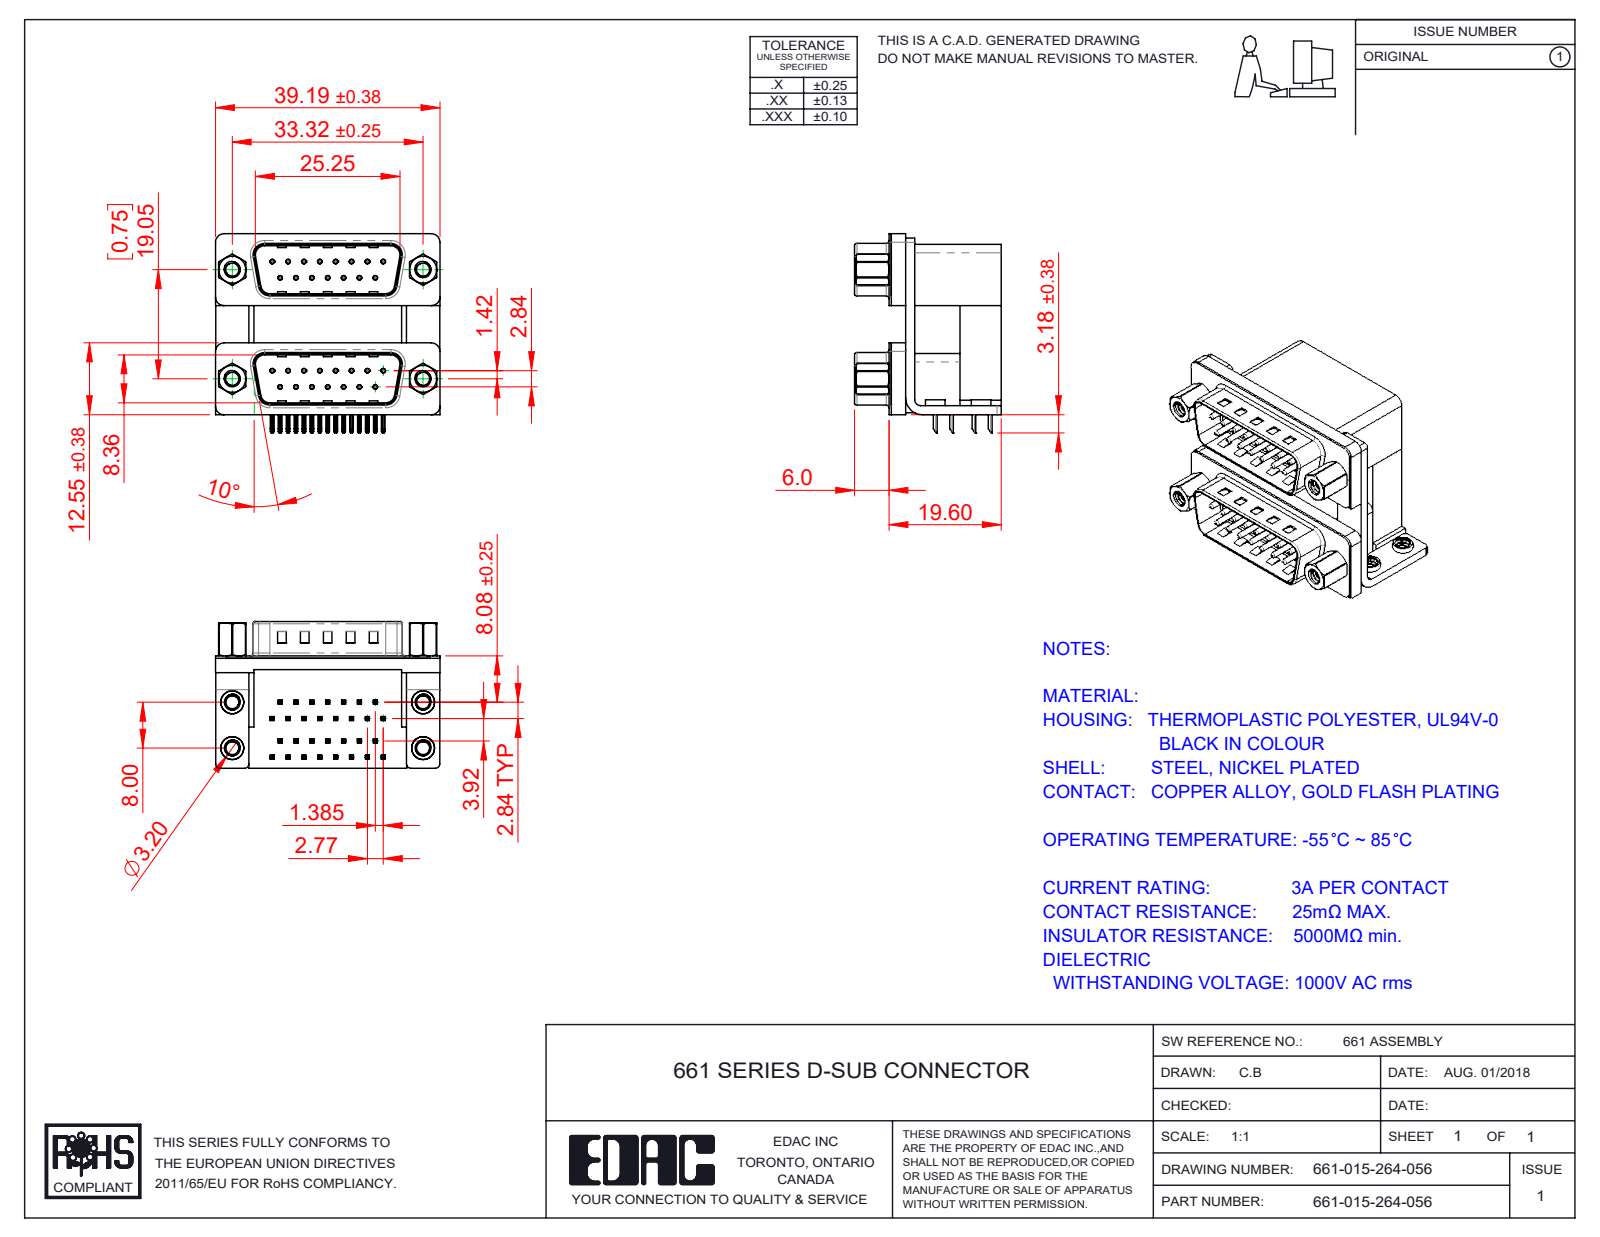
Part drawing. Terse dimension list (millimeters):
name: 661 4-40 Hex Standoff 5; 661 4-40 Threaded Board Mount; 661 Housing Spacer_15 Contacts M; 661-015-264-056 (+8 more)
written by: SolidWorks 2020 (CONFIG_CONTROL_DESIGN)
unit: mm
bodies: 49 solids, 3354 faces (1890 planar, 1074 cylindrical, 390 other)
size: 39.19 × 34.78 × 25.6
volume: 14 852 mm³; area: 16 879 mm²
holes: 30× ⌀0.35, 30× ⌀0.8, 8× ⌀2.26, 4× ⌀2.29, 4× ⌀2.75, 4× ⌀3.2, 4× ⌀3.5, 4× ⌀4, 4× ⌀4.8, 4× ⌀5
bosses: 30× ⌀0.75, 4× ⌀4.9, 4× ⌀4.75, 4× ⌀4, 4× ⌀3.9, 4× ⌀3.4, 4× ⌀2.79
rounds: 120× R0.25, 60× R0.12, 16× R0.5, 16× R1.5, 8× R0.75, 8× R0.9, 8× R1.6, 8× R2
face distances: 0.4, 19.05, 19.2, 10.69, 16.7, 2.5, 7.2, 12, 9.5, 2.9
hole spacings: 3.16, 2.77, 19.25, 5.54, 19.84, 8.31, 20.78, 19.05
